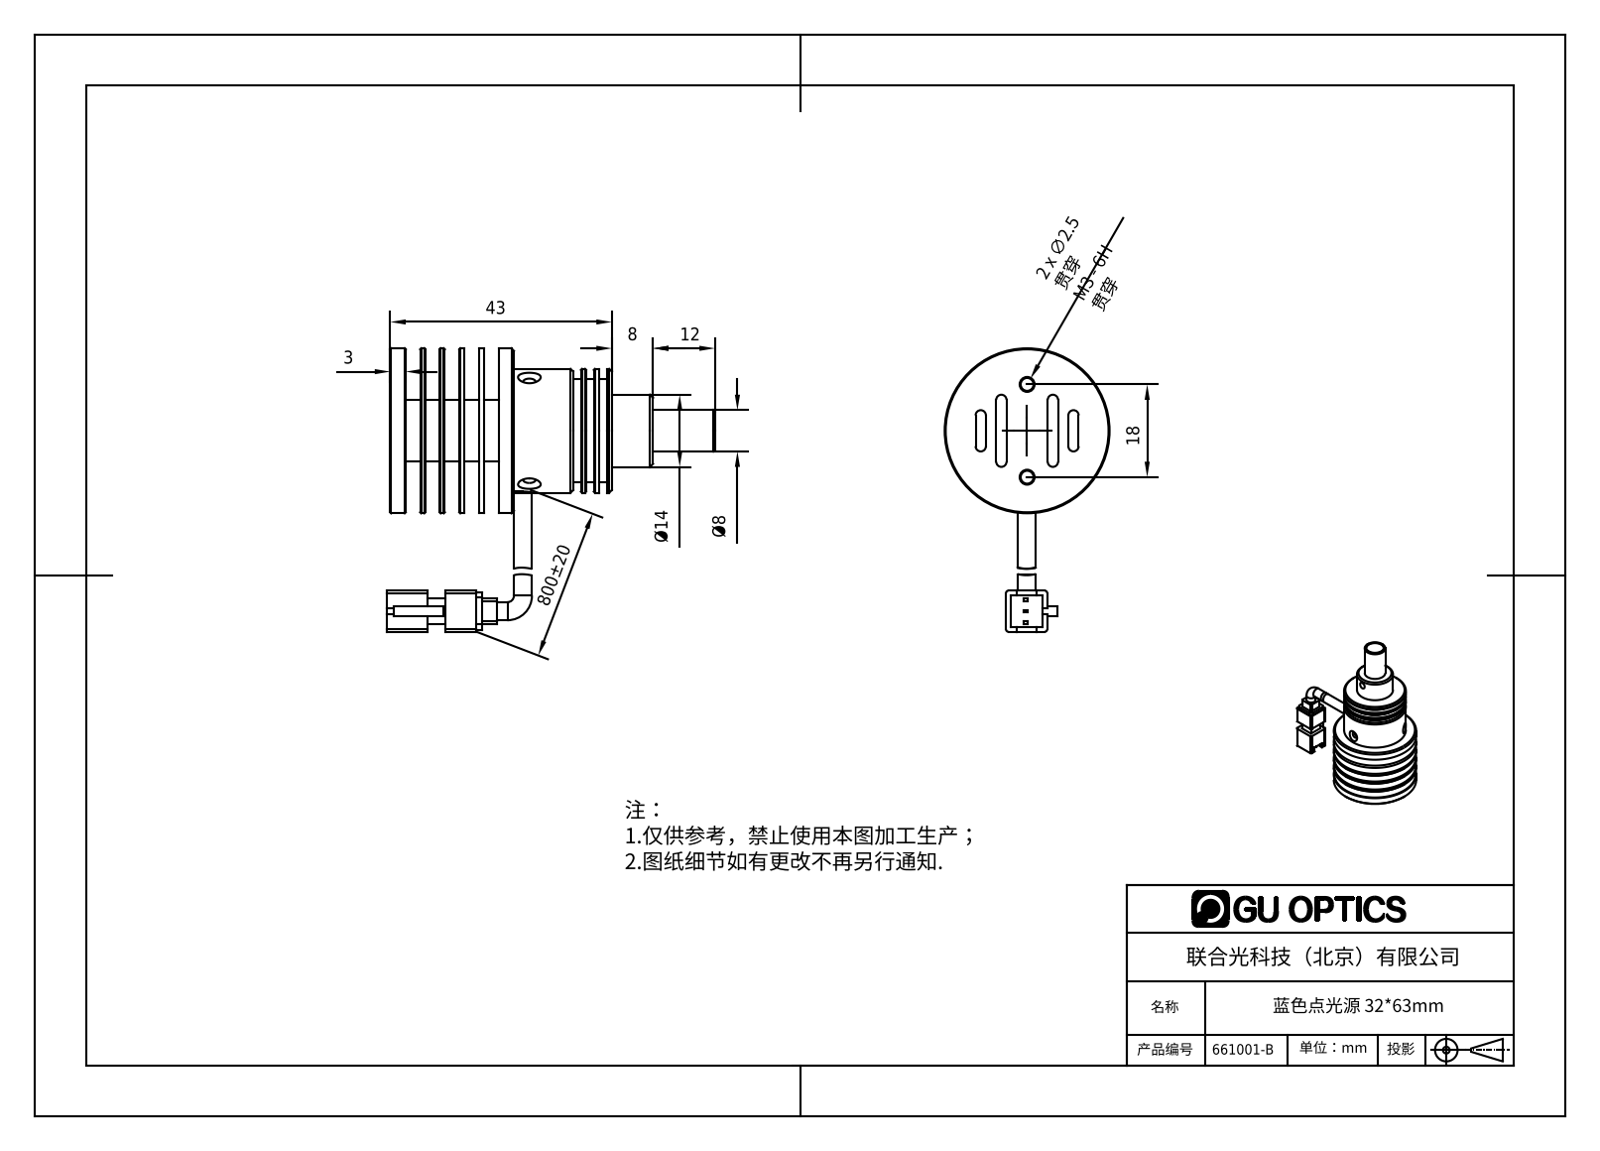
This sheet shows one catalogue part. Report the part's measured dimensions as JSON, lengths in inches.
{"part_name": "661001-B", "step_written_by": "SolidWorks 2016 (AUTOMOTIVE_DESIGN)", "units": "inches", "bodies": {"solids": 10, "faces": 401, "planar": 157, "cylindrical": 168, "other": 76}, "overall_size": [2.51, 2.165, 1.26], "volume_in3": 1.082, "surface_area_in2": 30.54, "round_holes": [[0.063, 7], [0.079, 3], [0.094, 3], [0.098, 3], [0.087, 2], [0.244, 1], [0.268, 1], [0.622, 1], [0.661, 1], [0.752, 1], [0.791, 1]], "round_bosses_or_shafts": [[0.138, 2], [1.26, 1], [0.945, 1], [0.787, 1], [0.669, 1], [0.614, 1], [0.567, 1], [0.551, 1]], "partial_cylinders_radius": [[0.039, 12], [0.02, 8], [0.059, 3], [0.065, 1]], "face_to_face_distances": [0.15, 0.11, 0.299, 0.039, 0.26, 0.153, 0.303, 0.189, 0.452, 0.409], "hole_center_spacings": [0.334, 0.236, 0.251, 0.548, 0.354, 0.473, 0.237, 0.251]}
